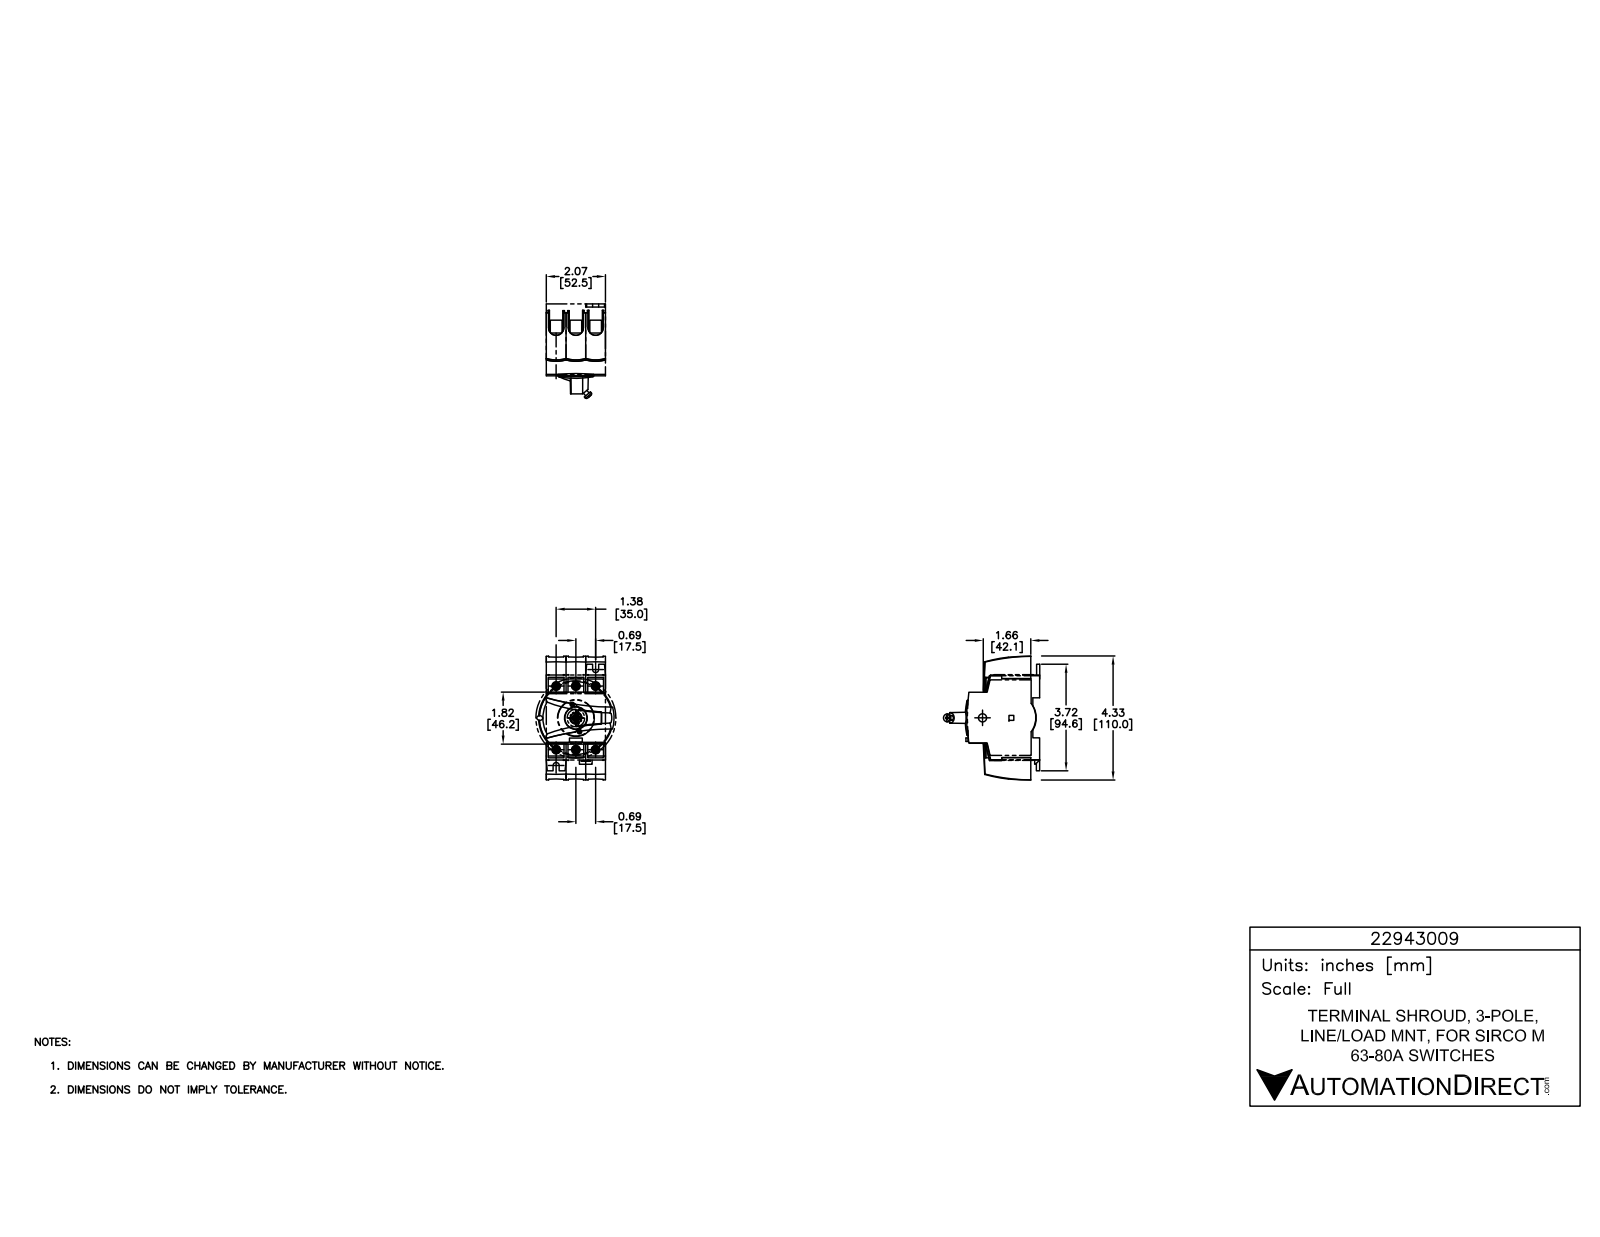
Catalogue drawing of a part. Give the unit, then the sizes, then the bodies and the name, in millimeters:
Units: millimetres
Overall size (bounding box): 52.5 × 43 × 31.9
Partial cylindrical surfaces — rounded edges, fillets, slot ends (radius × count): R6.7 ×3, R9.2 ×3, R0.5 ×1
Main face-to-face distances: 1.2, 34.4, 16.9, 17.5, 51.3, 18.1, 33.2, 35.6, 15.7, 52.5
Volume: 6 850 mm³ · Surface area: 11 550 mm²
Bodies: 1 solid, 72 faces (35 planar, 7 cylindrical, 30 other)
Part name (STEP PRODUCT): 22943009
STEP written by: SolidWorks 2015 (AUTOMOTIVE_DESIGN)
